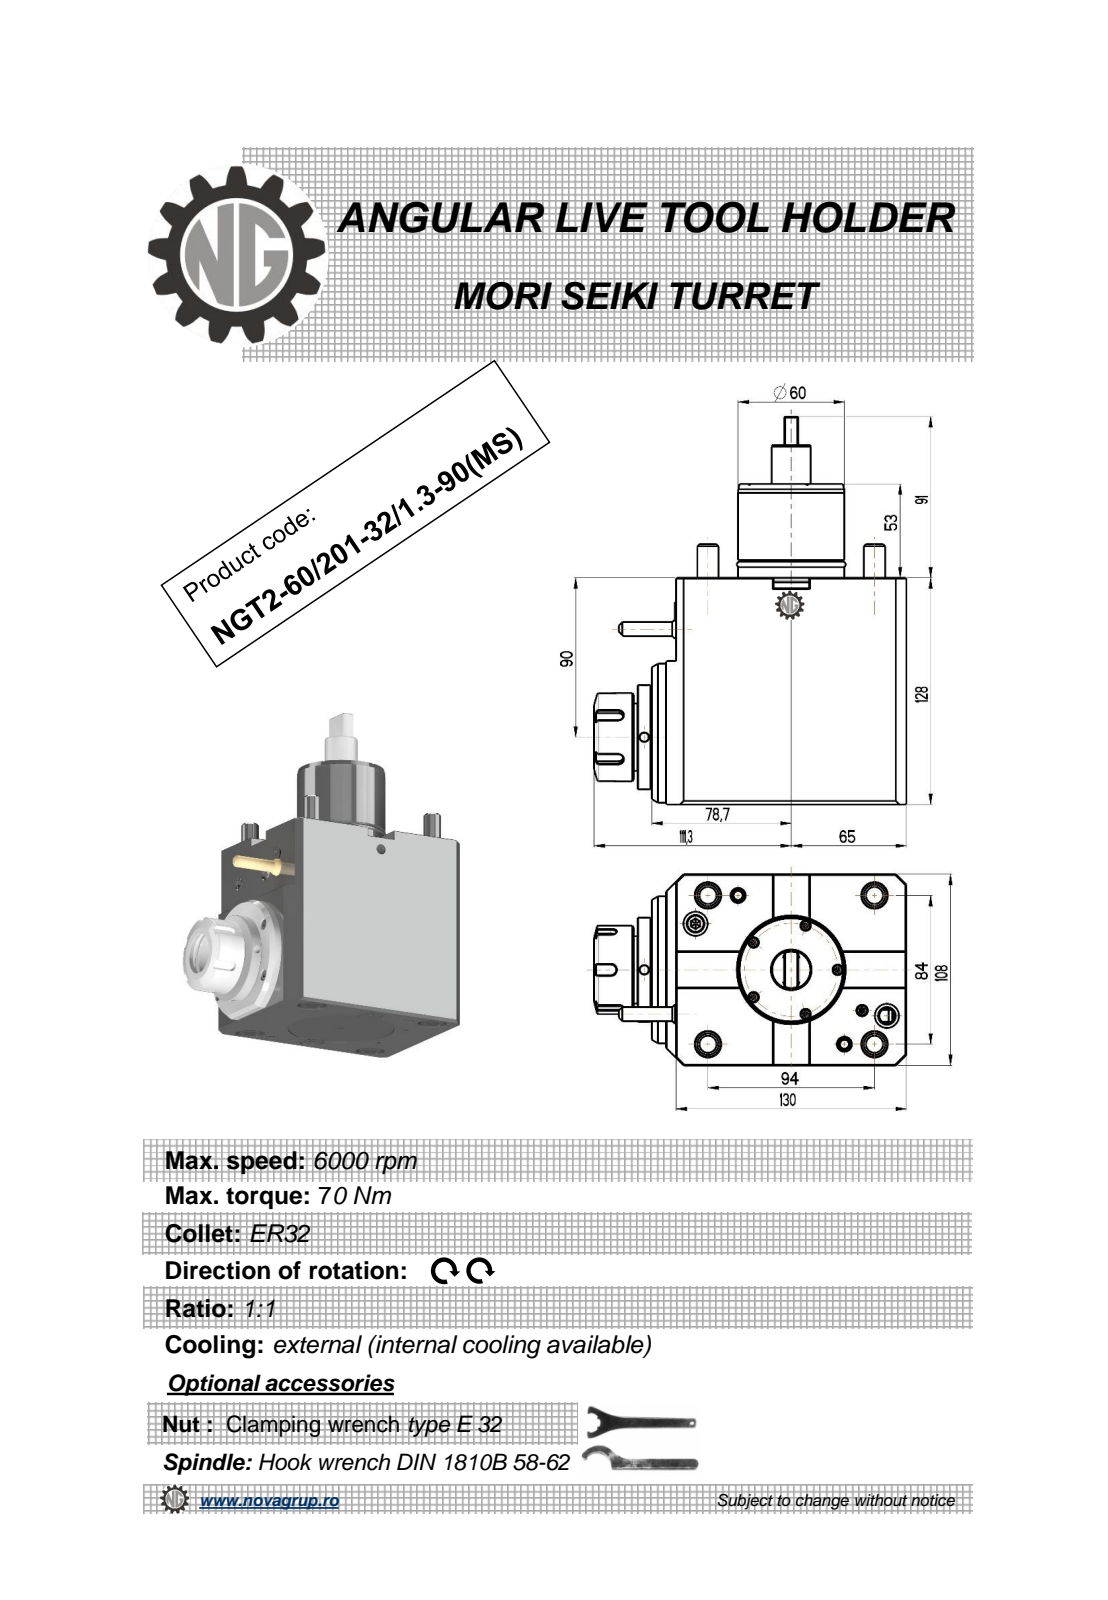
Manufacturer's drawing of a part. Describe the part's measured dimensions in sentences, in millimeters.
The part is named "NGT2_60_201_32_1_3_90_MS". Its 3-D file was written by "PRO/ENGINEER BY PARAMETRIC TECHNOLOGY CORPORATION, 2010280 (CONFIG_CONTROL_DESIGN)". It is 2 solids with 326 faces: 142 planar, 88 cylindrical and 96 other. Overall it measures 219 by 176.3 by 109.6 millimeters. Its volume is 2 060 000 cubic millimeters and its surface area 121 261 square millimeters. Round holes: 3 of diameter 5, 2 of diameter 13.6, 1 of diameter 3, 1 of diameter 8.5, 1 of diameter 27, 1 of diameter 58, 1 of diameter 70. Round bosses or shafts: 4 of diameter 12, 1 of diameter 83, 1 of diameter 60, 1 of diameter 59.8, 1 of diameter 57.4, 1 of diameter 55.4, 1 of diameter 50, 1 of diameter 48. Partial cylindrical surfaces (rounded edges, fillets, slot ends): 6 of radius 0.22, 6 of radius 0.51, 5 of radius 3, 2 of radius 0.8, 1 of radius 10.75. The main face-to-face distances are 108, 128, 6, 130, 124, 13.7, 137.7, 143.7, 122, 53. The hole center spacings are 59.93, 38.91, 65.92, 82.95, 119.87, 139.4.
